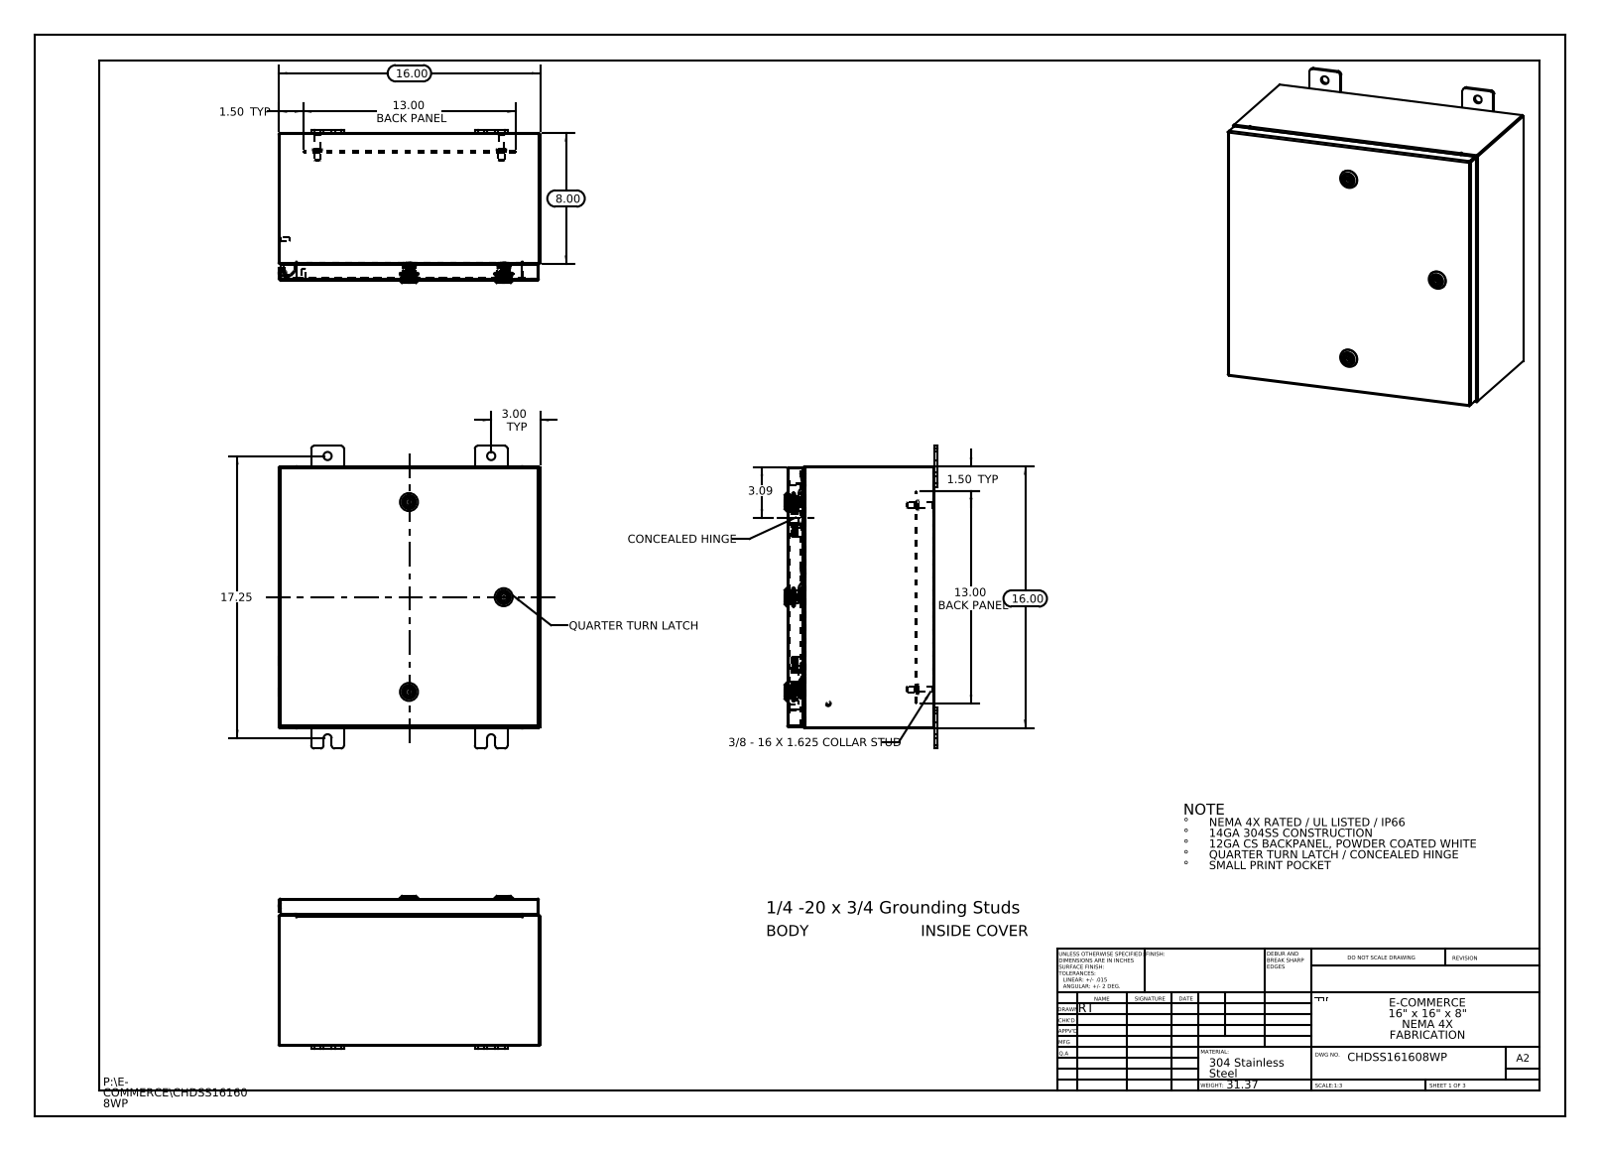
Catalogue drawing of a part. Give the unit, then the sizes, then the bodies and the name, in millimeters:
Units: millimetres
Overall size (bounding box): 469.9 × 406.4 × 237.6
Round holes (diameter × count): ⌀12.7 ×8, ⌀3.5 ×4, ⌀5 ×3, ⌀10 ×3, ⌀10.2 ×3, ⌀16 ×3, ⌀20 ×3, ⌀5.4 ×2
Round bosses / shafts (diameter × count): ⌀6 ×5, ⌀15.9 ×4, ⌀9.5 ×4, ⌀8.4 ×4, ⌀28 ×3, ⌀19.8 ×3, ⌀15.9 ×3, ⌀15.5 ×3
Partial cylindrical surfaces — rounded edges, fillets, slot ends (radius × count): R0.2 ×99, R3 ×99, R0.7 ×36, R4.8 ×24, R0.3 ×18, R2.2 ×18, R0.5 ×12, R5 ×12
Main face-to-face distances: 1.9, 404.5, 1.9, 402.6, 406.4, 228.9, 226.9, 227, 225.1, 25.4
Hole centre spacings: 47.2, 77.9, 142.9, 254, 285.8, 285.8, 322.6, 330.6
Volume: 1 837 000 mm³ · Surface area: 1 829 000 mm²
Bodies: 37 solids, 2966 faces (938 planar, 930 cylindrical, 1098 other)
Part name (STEP PRODUCT): CHDSS161608WP; Quarter-20 CD Stud; Concealed Hinge (Cover Side); Washer-221320-IB-Industrilas_Washer-221320-IB-Industrilas (+8 more)
STEP written by: SolidWorks 2013 (CONFIG_CONTROL_DESIGN)
